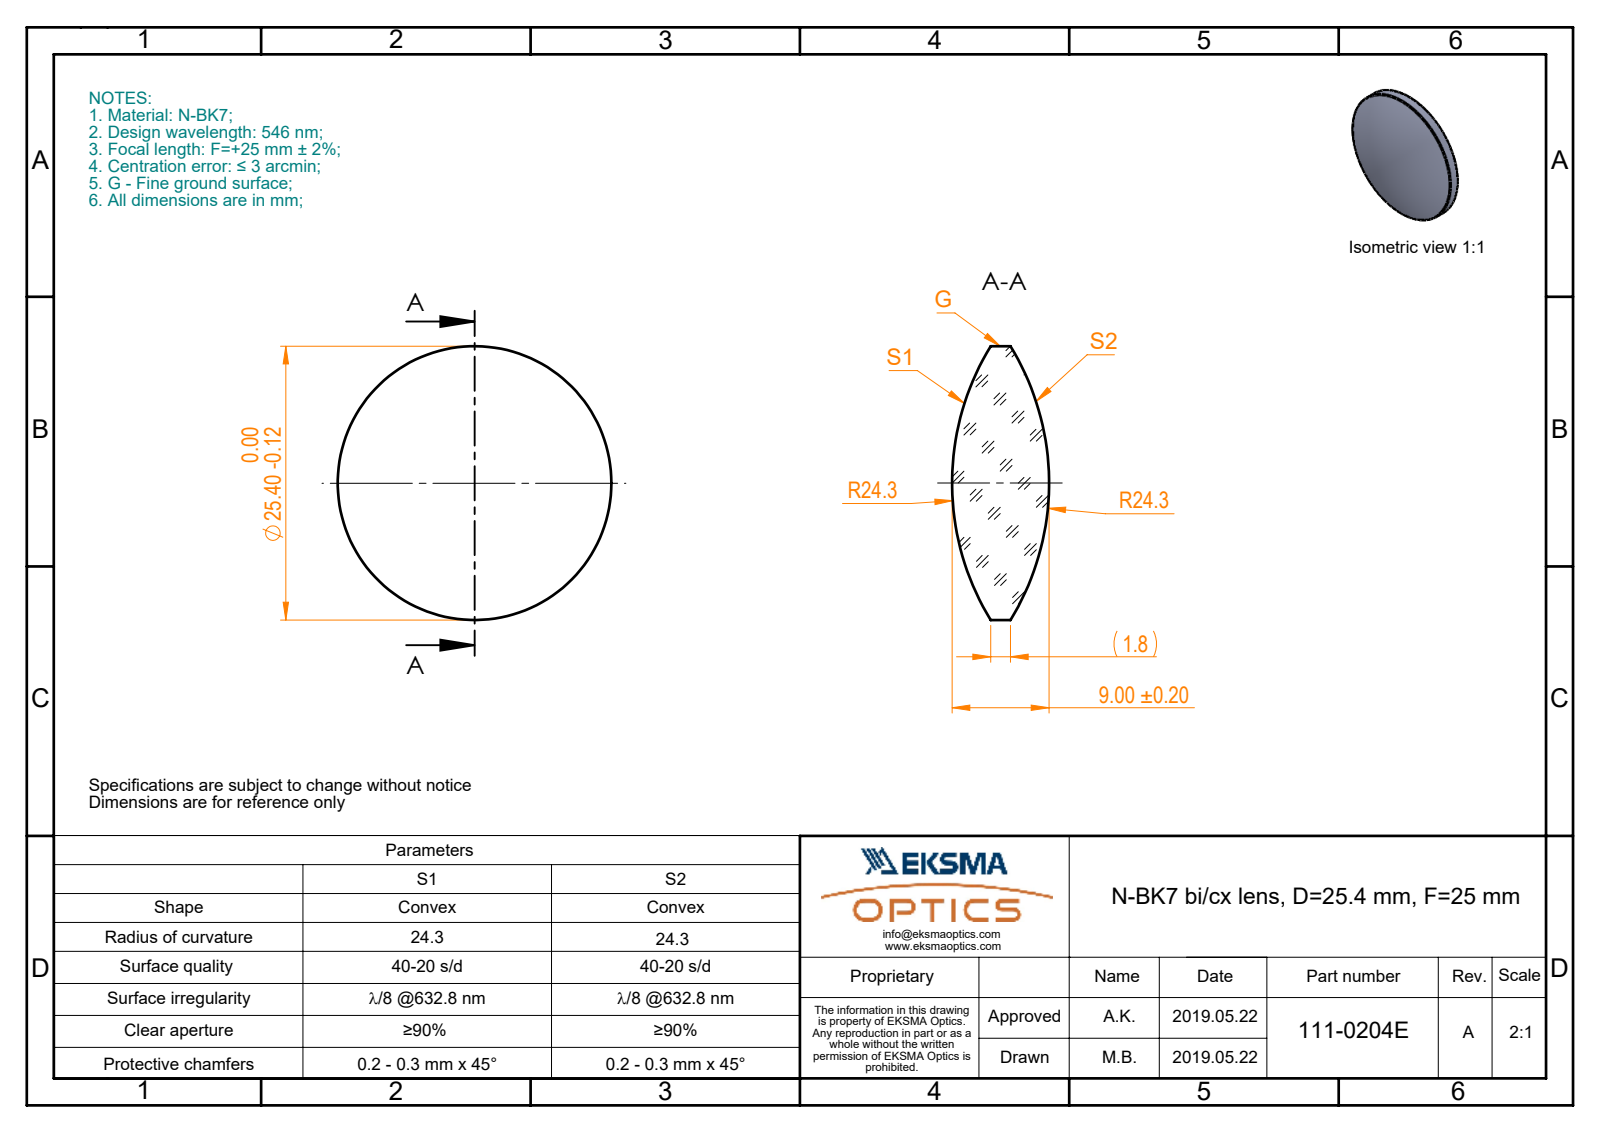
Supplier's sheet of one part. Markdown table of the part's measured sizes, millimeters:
| quantity | value |
| --- | --- |
| part name | 111-0204E BK7 bi-cx 25.4 F25 |
| STEP written by | SolidWorks 2017 (CONFIG_CONTROL_DESIGN) |
| units | millimeters |
| bodies | 1 solid, 6 faces (0 planar, 2 cylindrical, 4 other) |
| overall size | 25.4 × 25.4 × 9 |
| volume | 2 793 mm³ |
| surface area | 1 240 mm² |
| round bosses / shafts (diameter × count) | 25.4 × 1 |
